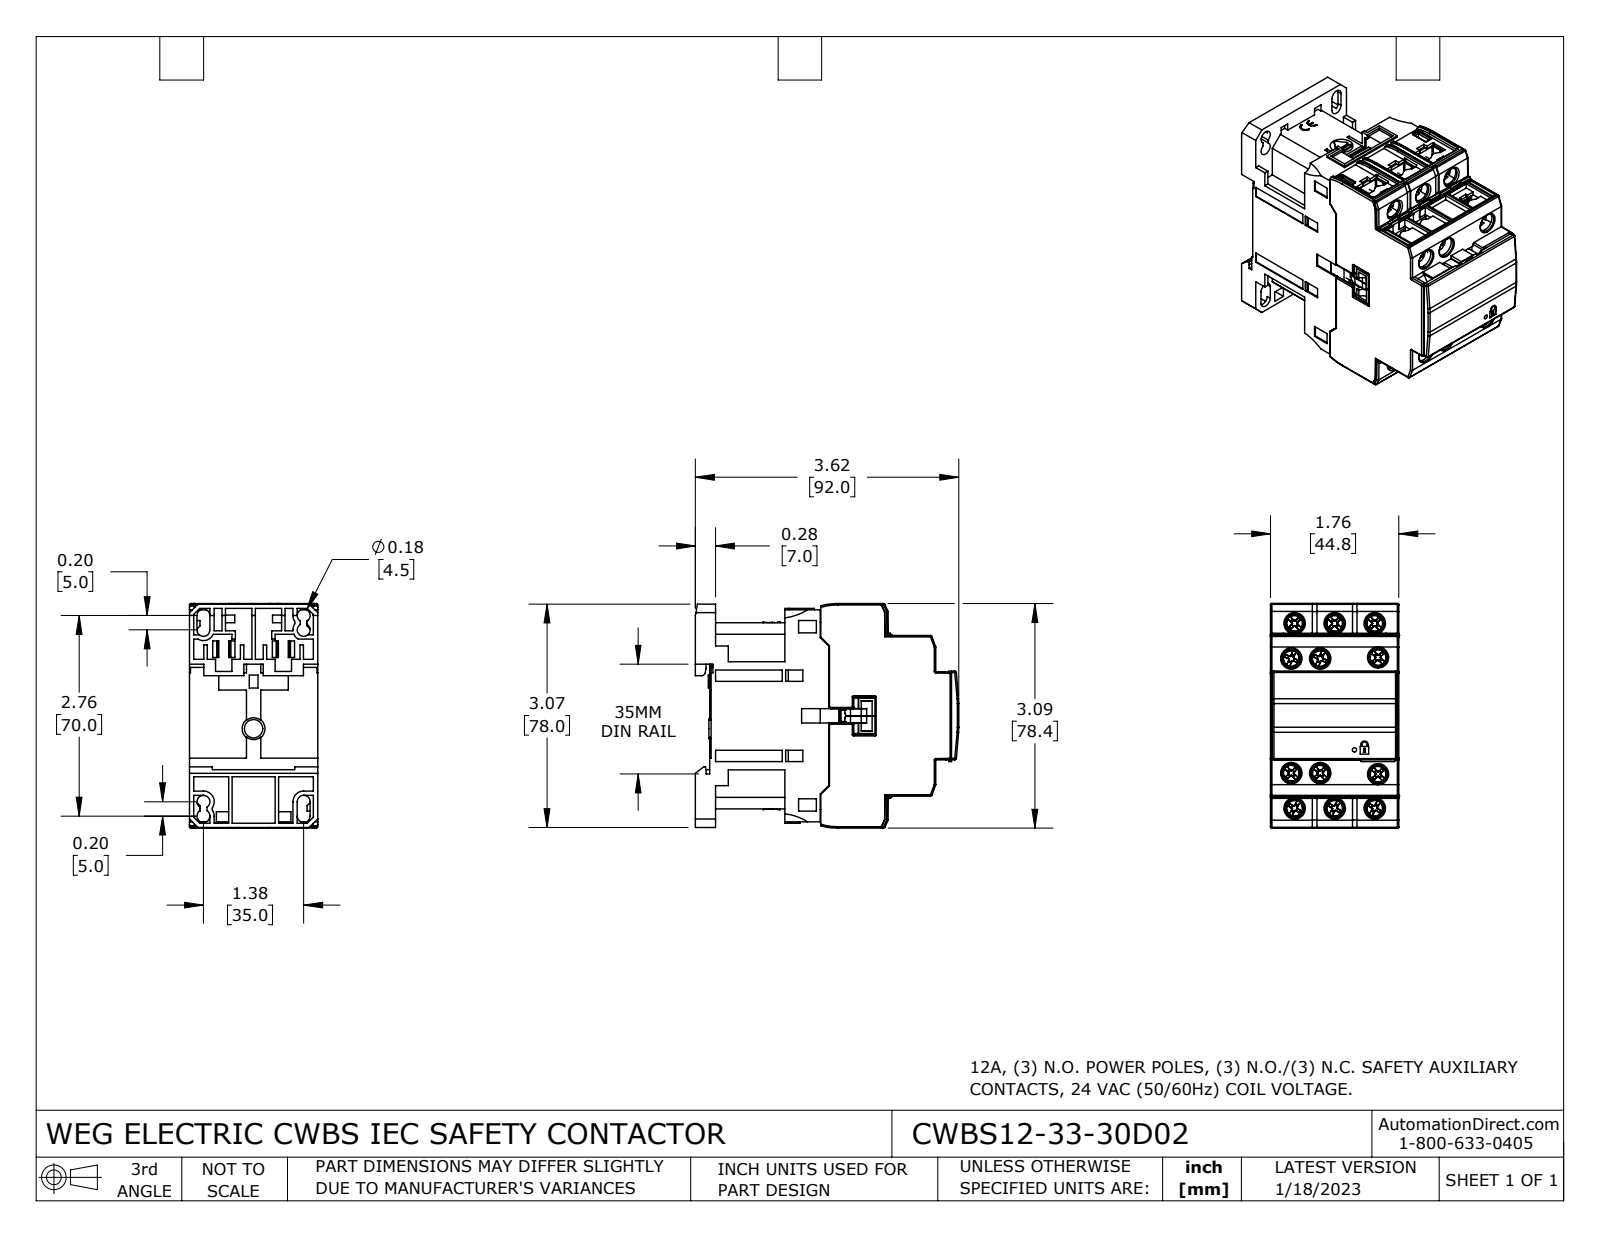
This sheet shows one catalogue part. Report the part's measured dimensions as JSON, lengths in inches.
{"part_name": "CWBS12-33-30D02", "step_written_by": "SolidWorks 2021 (CONFIG_CONTROL_DESIGN)", "units": "inches", "bodies": {"solids": 45, "faces": 3295, "planar": 2311, "cylindrical": 624, "other": 360}, "overall_size": [3.62, 3.087, 1.764], "volume_in3": 13.51, "surface_area_in2": 120.4, "round_holes": [[0.124, 12], [0.256, 6], [0.177, 4], [0.059, 1]], "round_bosses_or_shafts": [[0.169, 12], [0.138, 12], [0.107, 8], [0.107, 4]], "partial_cylinders_radius": [[0.02, 139], [0.012, 52], [0.071, 24], [0.964, 24], [2.128, 24], [0.016, 20], [0.039, 19], [0.106, 11]], "face_to_face_distances": [1.764, 0.047, 1.717, 3.305, 1.754, 1.551, 0.276, 0.022, 1.776, 1.53], "hole_center_spacings": [0.551, 1.102, 0.197, 0.398, 0.795, 1.193, 1.341, 1.575]}
